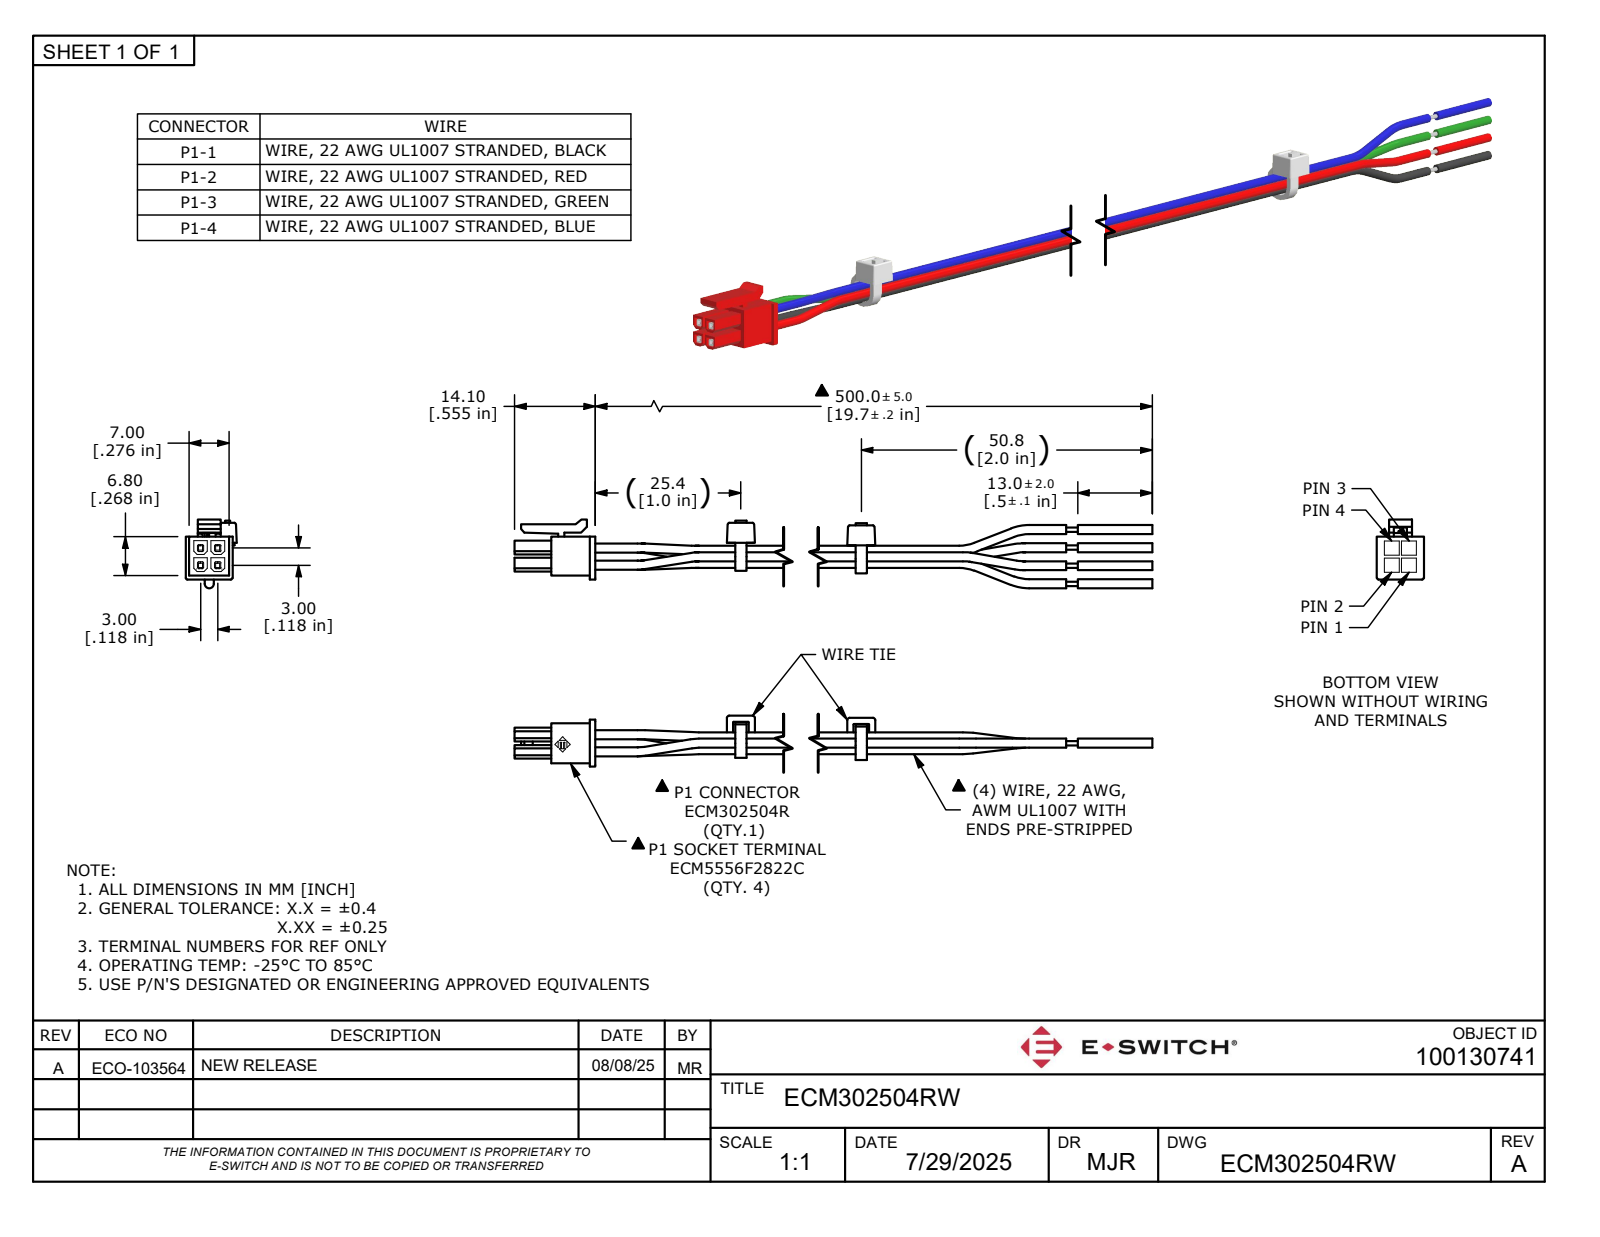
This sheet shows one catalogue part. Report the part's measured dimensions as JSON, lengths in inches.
{"part_name": "ECM302504RW", "step_written_by": "Autodesk Inventor 2022 (AUTOMOTIVE_DESIGN)", "units": "inches", "bodies": {"solids": 2, "faces": 1370, "planar": 684, "cylindrical": 470, "other": 216}, "overall_size": [20.24, 0.473, 0.351], "volume_in3": 0.272, "surface_area_in2": 18.43, "round_holes": [[0.016, 4]], "round_bosses_or_shafts": [[0.062, 20], [0.03, 4]], "partial_cylinders_radius": [[0.008, 84], [0.01, 36], [0.016, 20], [0.008, 16], [0.007, 8], [0.006, 6], [0.012, 6], [0.063, 6]], "face_to_face_distances": [0.118, 0.018, 0.028, 0.059, 0.104, 0.014, 0.033, 0.163, 0.045, 0.185], "hole_center_spacings": [0.024, 0.118, 0.12]}
